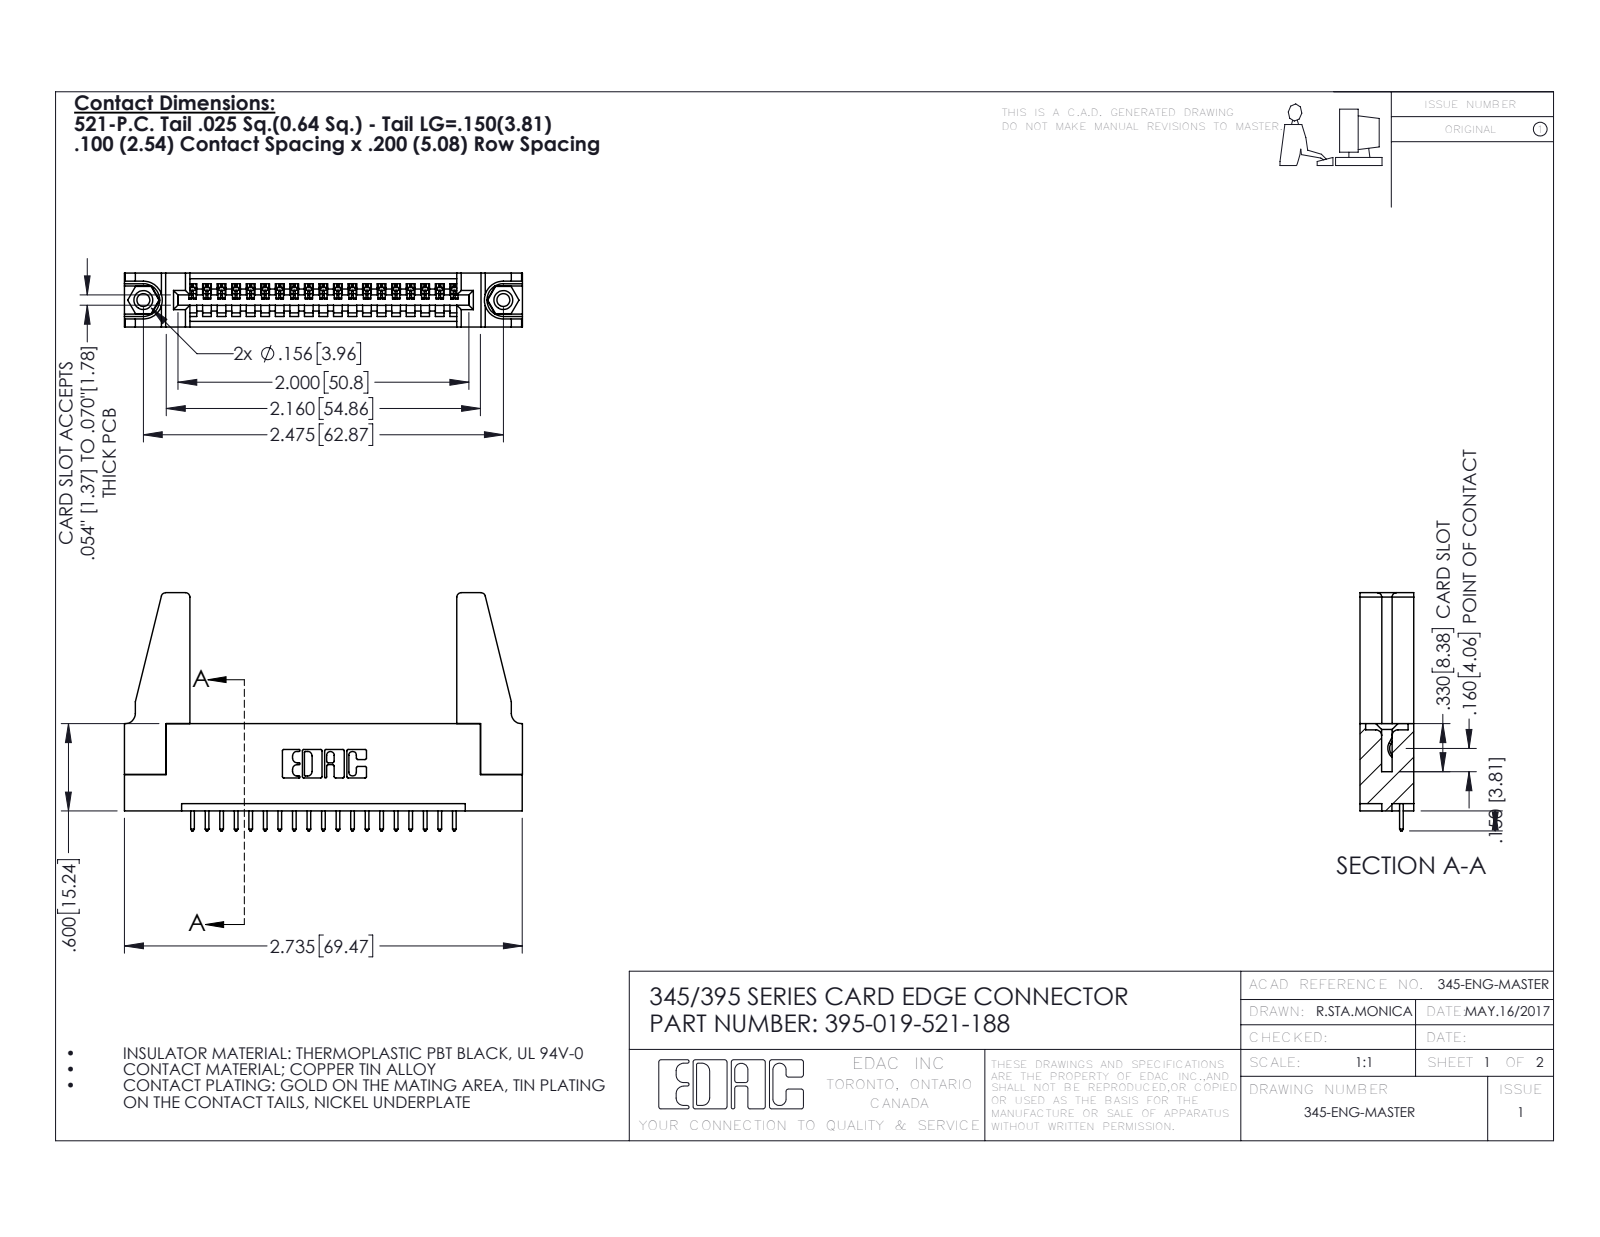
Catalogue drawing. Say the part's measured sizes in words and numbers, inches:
The part is named "345-250-001_345-250-001-102; 345 Part_Flush Mounting Lugs - 0.156 Dia-TH; 345-220-078_345-220-088; 345-292-001_345-293-121 (+1 more)". Its 3-D file was written by "SolidWorks 2016 (CONFIG_CONTROL_DESIGN)". It is 24 solids with 1352 faces: 912 planar, 424 cylindrical and 16 other. Overall it measures 2.736 by 1.637 by 0.37 inches. Its volume is 0.586 cubic inches and its surface area 17.13 square inches. Round holes: 2 of diameter 0.089, 2 of diameter 0.125, 2 of diameter 0.156, 1 of diameter 0.064. Round bosses or shafts: 2 of diameter 0.155. Partial cylindrical surfaces (rounded edges, fillets, slot ends): 38 of radius 0.006, 38 of radius 0.01, 22 of radius 0.01, 8 of radius 0.03, 6 of radius 0.007, 6 of radius 0.031, 3 of radius 0.026, 2 of radius 0.031. The main face-to-face distances are 0.37, 0.072, 0.298, 0.2, 0.098, 0.272, 0.025, 0.225, 0.148, 0.15. The hole center spacings are 0.27, 2.241, 2.475.
